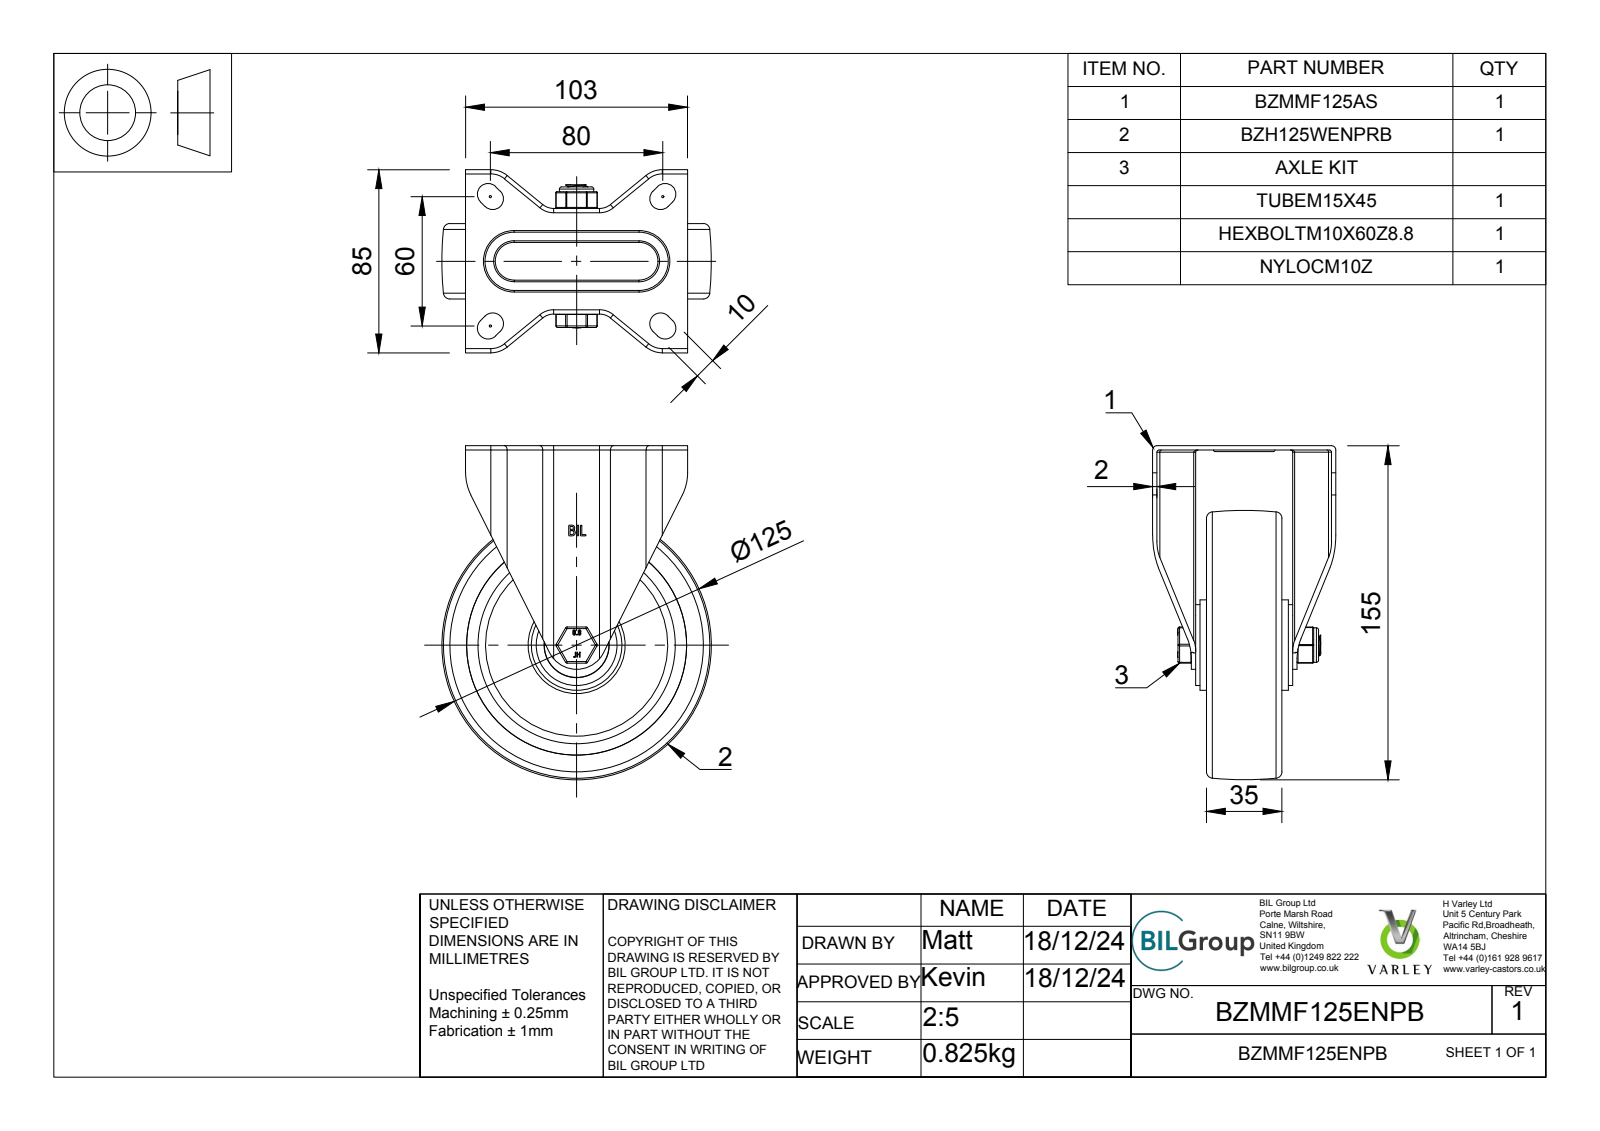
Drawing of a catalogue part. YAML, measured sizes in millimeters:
part_name: "BZMMF125ENPB v3; BZMMF125AS v1; BZMMF125AS; ZINC PLATED, PRESSED STEEL BRACKET (+8 more)"
step_written_by: "Autodesk Translation Framework v13.20.0.188 (AP242_MANAGED_MODEL_BASED_3D_ENGINEERING_MIM_LF)"
units: millimeters
bodies: {solids: 17, faces: 491, planar: 208, cylindrical: 181, other: 102}
overall_size: [155, 125, 85]
volume: 336078
surface_area: 139835
round_holes:
  - {diameter: 10, count: 1}
  - {diameter: 10.2, count: 1}
  - {diameter: 12, count: 1}
  - {diameter: 15.5, count: 1}
  - {diameter: 16, count: 1}
  - {diameter: 25.5, count: 1}
  - {diameter: 30.2, count: 1}
  - {diameter: 91.5, count: 1}
  - {diameter: 102, count: 1}
round_bosses_or_shafts:
  - {diameter: 5, count: 8}
  - {diameter: 42, count: 1}
  - {diameter: 37.5, count: 1}
  - {diameter: 30, count: 1}
  - {diameter: 24.75, count: 1}
  - {diameter: 14.95, count: 1}
  - {diameter: 9.85, count: 1}
  - {diameter: 8.14, count: 1}
partial_cylinders:
  - {radius: 0.75, count: 20}
  - {radius: 0.5, count: 18}
  - {radius: 1, count: 8}
  - {radius: 2, count: 8}
  - {radius: 5, count: 8}
  - {radius: 4, count: 4}
  - {radius: 6, count: 4}
  - {radius: 8, count: 4}
face_to_face_distances: [2, 21, 7, 14, 40, 5, 19, 26, 18.84, 28]
